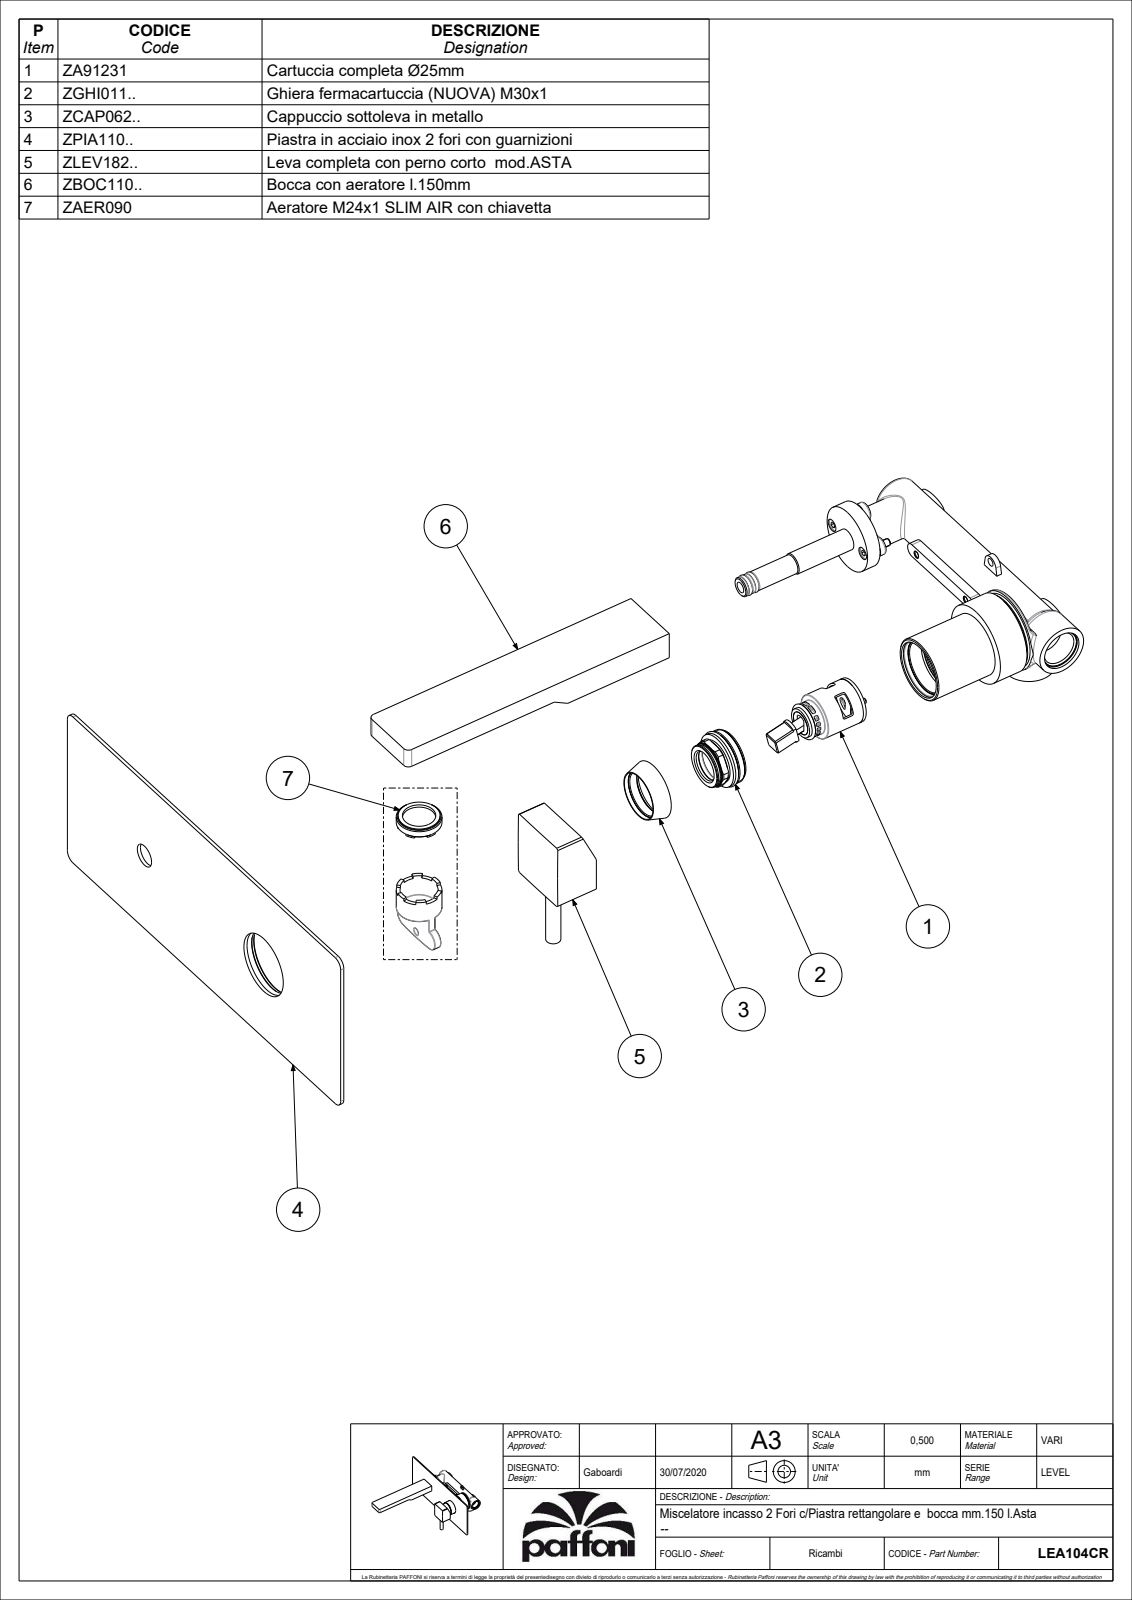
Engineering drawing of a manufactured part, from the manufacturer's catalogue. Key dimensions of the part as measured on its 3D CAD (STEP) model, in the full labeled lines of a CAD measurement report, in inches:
Part name (STEP PRODUCT): LEA104CR
STEP written by: CREO PARAMETRIC BY PTC INC, 2020044 (CONFIG_CONTROL_DESIGN)
Units: inches
Bodies: 2 solids, 677 faces (210 planar, 252 cylindrical, 215 other)
Overall size (bounding box): 9.843 × 6.693 × 4.337
Volume: 9.524 in³ · Surface area: 149.9 in²
Round holes (diameter × count): ⌀0.236 ×2, ⌀0.433 ×2, ⌀0.323 ×1, ⌀0.472 ×1, ⌀0.512 ×1, ⌀0.591 ×1, ⌀0.657 ×1, ⌀0.669 ×1, ⌀0.689 ×1, ⌀0.756 ×1, ⌀0.795 ×1, ⌀0.894 ×1
Round bosses / shafts (diameter × count): ⌀1.386 ×1, ⌀1.181 ×1, ⌀1.091 ×1, ⌀0.984 ×1, ⌀0.937 ×1, ⌀0.886 ×1, ⌀0.787 ×1, ⌀0.748 ×1
Partial cylindrical surfaces — rounded edges, fillets, slot ends (radius × count): R0.02 ×56, R0.039 ×7, R0.079 ×4, R0.197 ×4, R0.083 ×3, R0.098 ×2, R0.118 ×2, R0.138 ×2
Main face-to-face distances: 0.079, 0.453, 0.197, 1.378, 0.65, 1.644, 2.293, 2.894, 4.272, 5.689
Hole centre spacings: 0.046, 4.291, 4.292, 6.257
